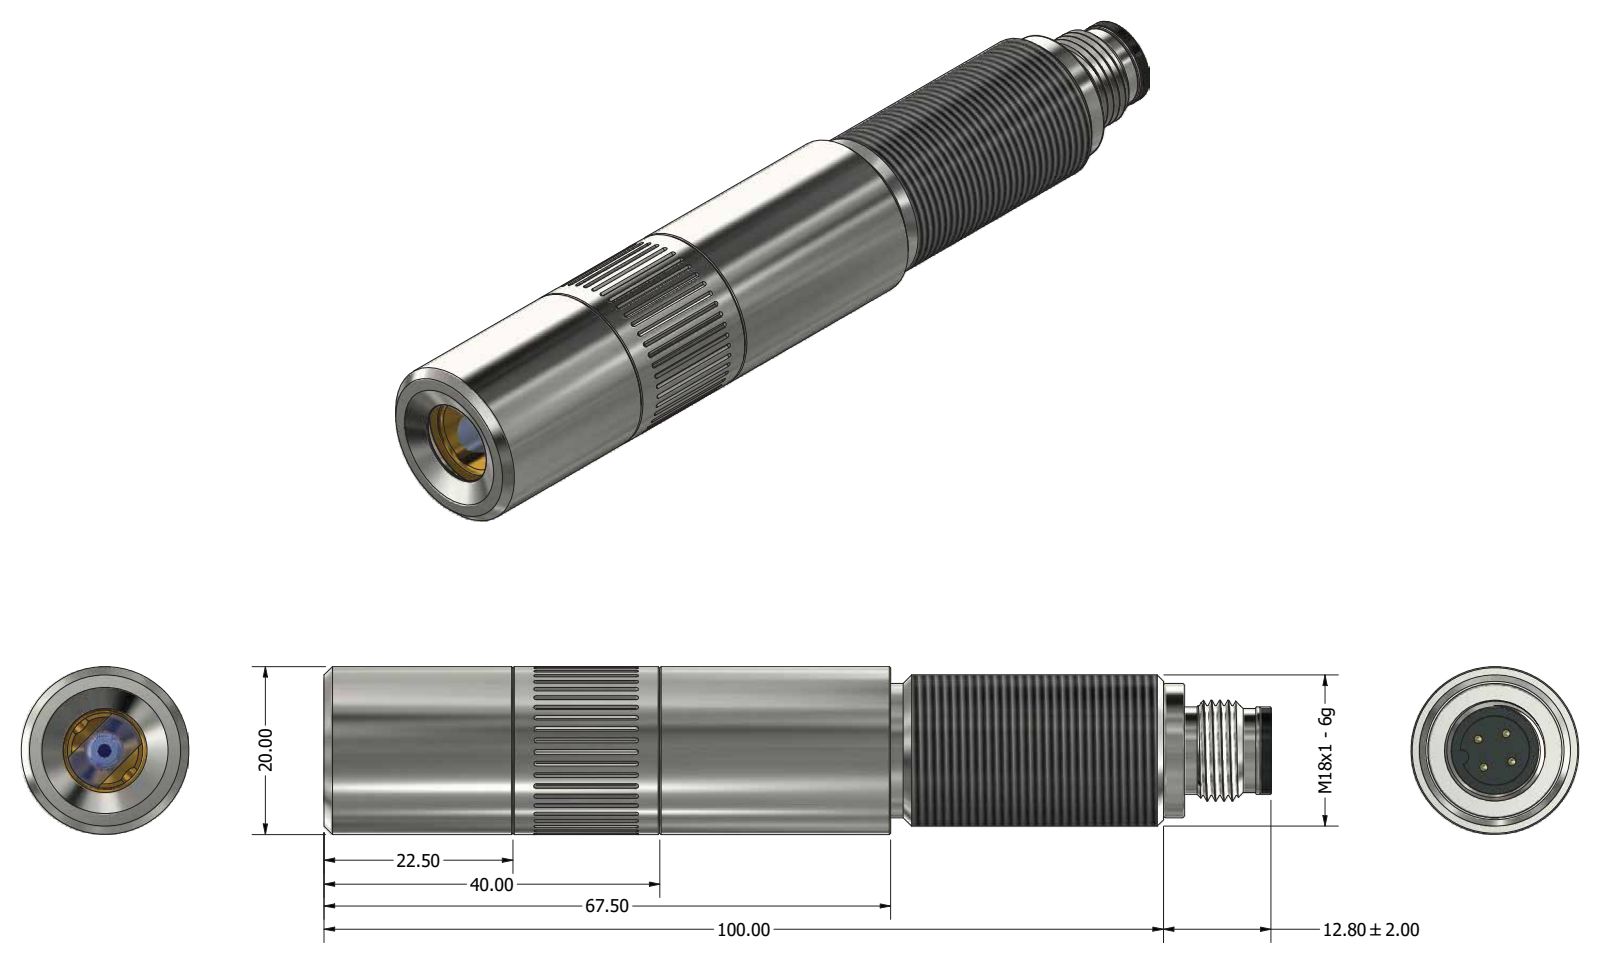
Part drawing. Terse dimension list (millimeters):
name: lwpro20-ea; back_m18; ext_ring_knurl; front (+1 more)
written by: unknown (AUTOMOTIVE_DESIGN)
unit: mm
bodies: 4 solids, 307 faces (113 planar, 50 cylindrical, 144 other)
size: 112.8 × 20 × 20
volume: 15 050 mm³; area: 13 499 mm²
holes: 4× ⌀0.75, 1× ⌀8.2, 1× ⌀10, 1× ⌀10.92, 1× ⌀12.5, 1× ⌀13, 1× ⌀14, 1× ⌀14.5, 1× ⌀17.75, 1× ⌀18
bosses: 4× ⌀1.5, 4× ⌀1, 1× ⌀20, 1× ⌀16, 1× ⌀12, 1× ⌀10.8, 1× ⌀10.4
rounds: 4× R4.54, 1× R0.9
face distances: 77.5, 2.5, 80, 35, 32.5, 45, 22.5, 3, 10.5, 8
hole spacings: 3.54, 2.5, 5, 2.49, 2.51
